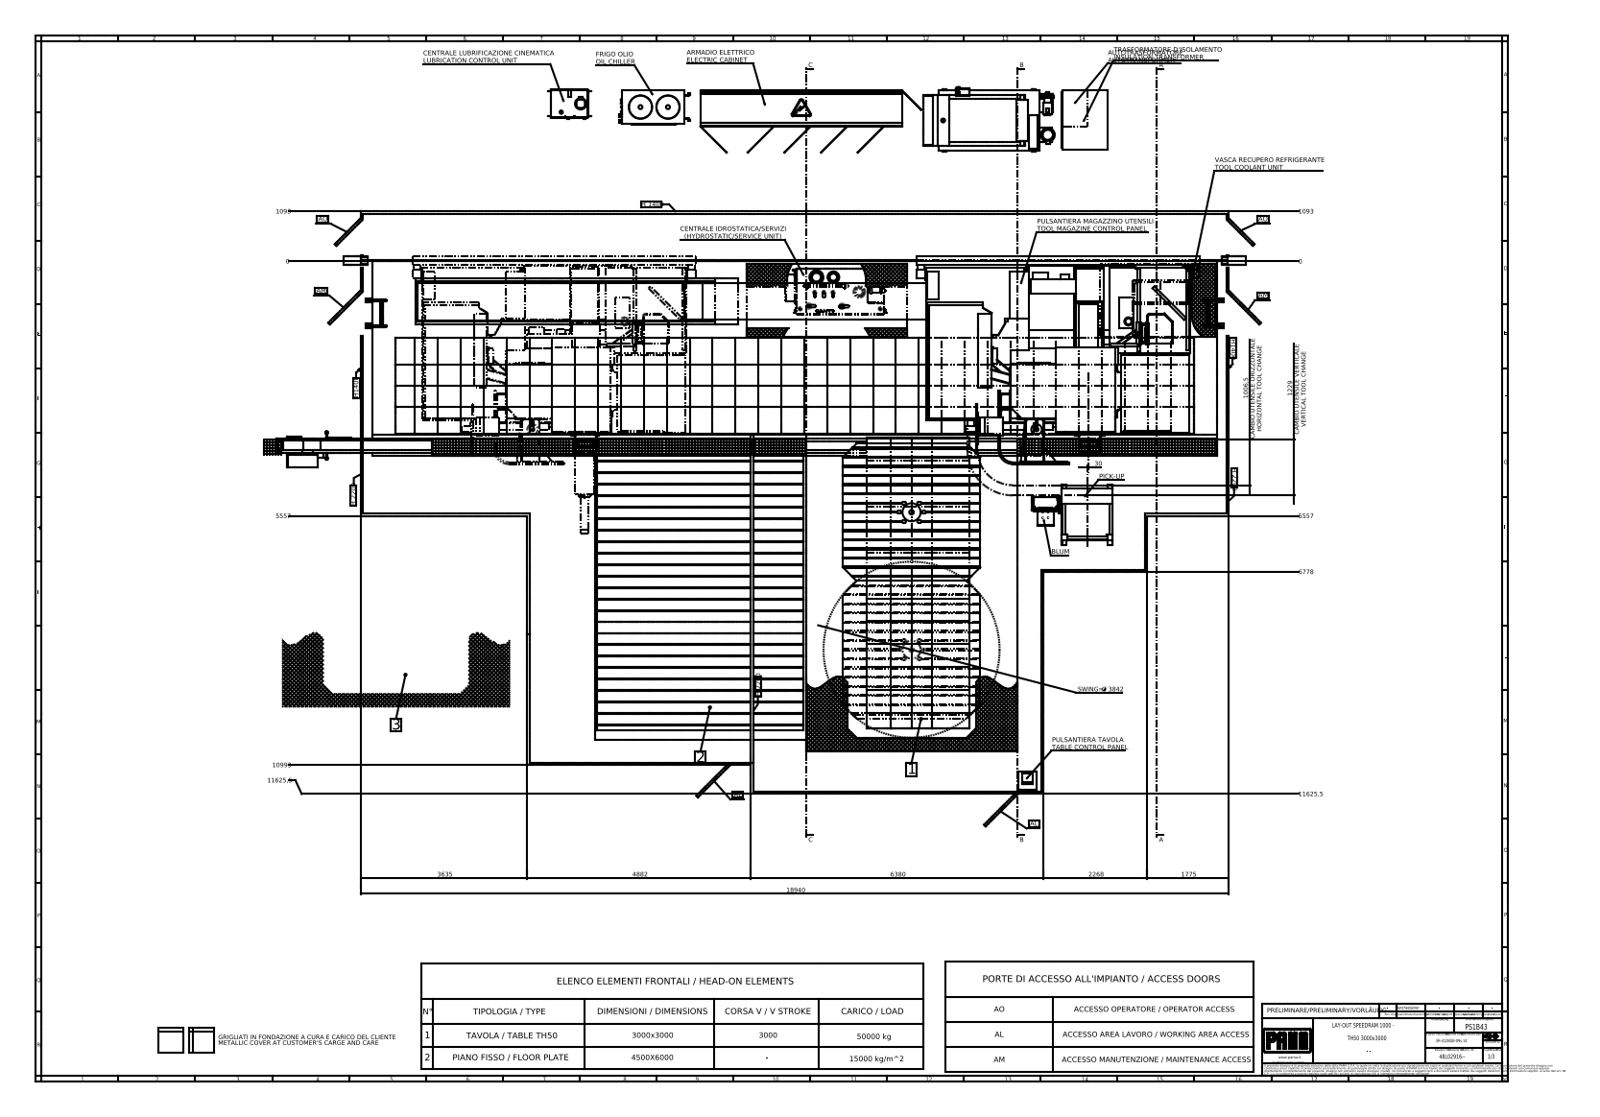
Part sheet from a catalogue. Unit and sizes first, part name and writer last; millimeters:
Units: millimetres
Overall size (bounding box): 22440 × 18380.5 × 10305
Round holes (diameter × count): ⌀69.6 ×183, ⌀35 ×152, ⌀37.2 ×18, ⌀5 ×17, ⌀30 ×11, ⌀7 ×9, ⌀14 ×8, ⌀11 ×7, ⌀8 ×6, ⌀340 ×5, ⌀6.6 ×4, ⌀12 ×4
Round bosses / shafts (diameter × count): ⌀42.4 ×18, ⌀60 ×11, ⌀40 ×11, ⌀150 ×10, ⌀55 ×8, ⌀35 ×6, ⌀12 ×6, ⌀250 ×5
Partial cylindrical surfaces — rounded edges, fillets, slot ends (radius × count): R5 ×184, R15 ×76, R35 ×60, R8 ×40, R6 ×28, R20 ×28, R4 ×24, R10 ×24
Main face-to-face distances: 2000, 50, 1247, 753, 10, 18318.5, 300, 22440, 1297, 304
Hole centre spacings: 273.13, 500, 1235.56, 758.02, 1423.59, 1000, 1254.83, 1739.71
Volume: 740 300 000 000 mm³ · Surface area: 2 560 000 000 mm²
Bodies: 509 solids, 8785 faces (6012 planar, 2231 cylindrical, 542 other)
Part name (STEP PRODUCT): S003412_H=1000; S003207_X=11000; S003389; S003265_Y=4500 (+8 more)
STEP written by: SolidWorks 2023 (AUTOMOTIVE_DESIGN)
